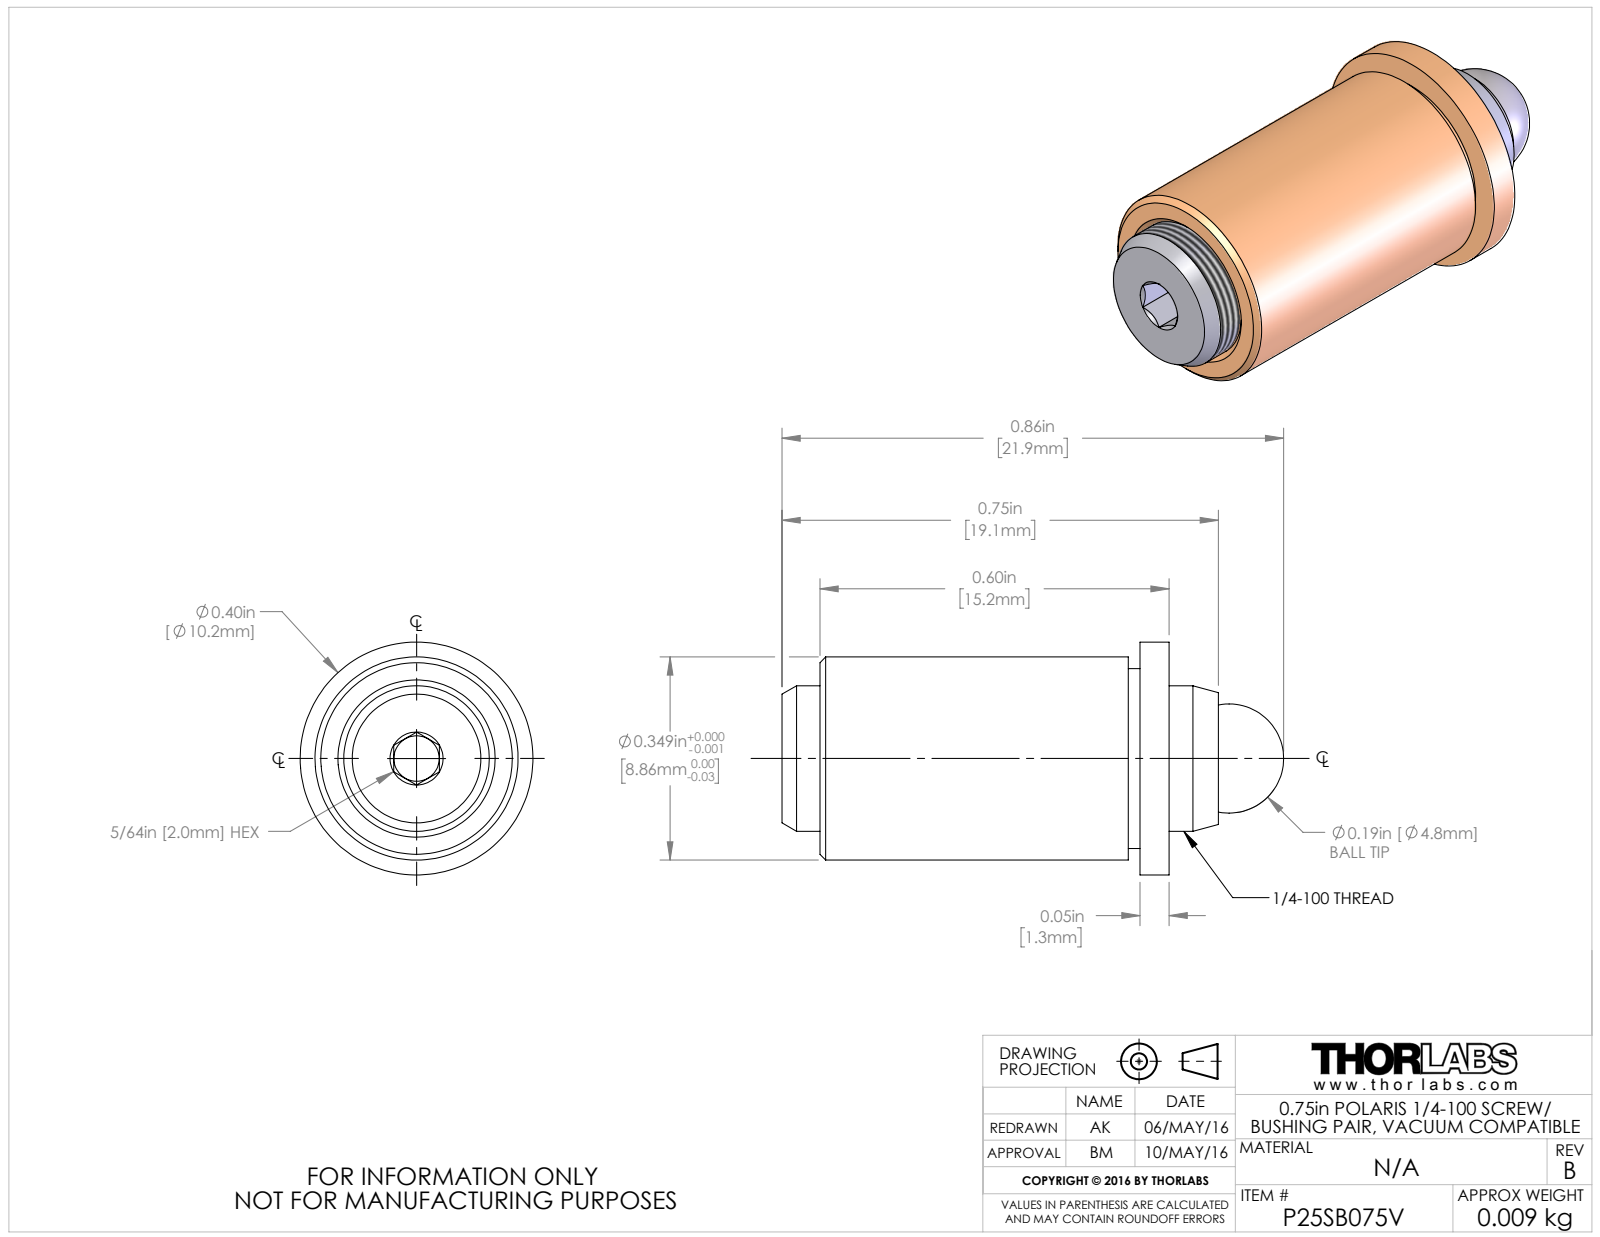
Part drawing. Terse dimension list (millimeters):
name: 22538-E0W
written by: SolidWorks 2018 (AUTOMOTIVE_DESIGN)
unit: mm
bodies: 3 solids, 45 faces (13 planar, 12 cylindrical, 20 other)
size: 21.89 × 10.16 × 10.16
volume: 1 080 mm³; area: 1 401 mm²
holes: 1× ⌀1.98, 1× ⌀6.35
bosses: 1× ⌀10.16, 1× ⌀8.86, 1× ⌀7.85
face distances: 1.27, 16.89, 15.62, 15.24, 13.97, 1.65, 1.78, 0.51, 13.46, 15.11
